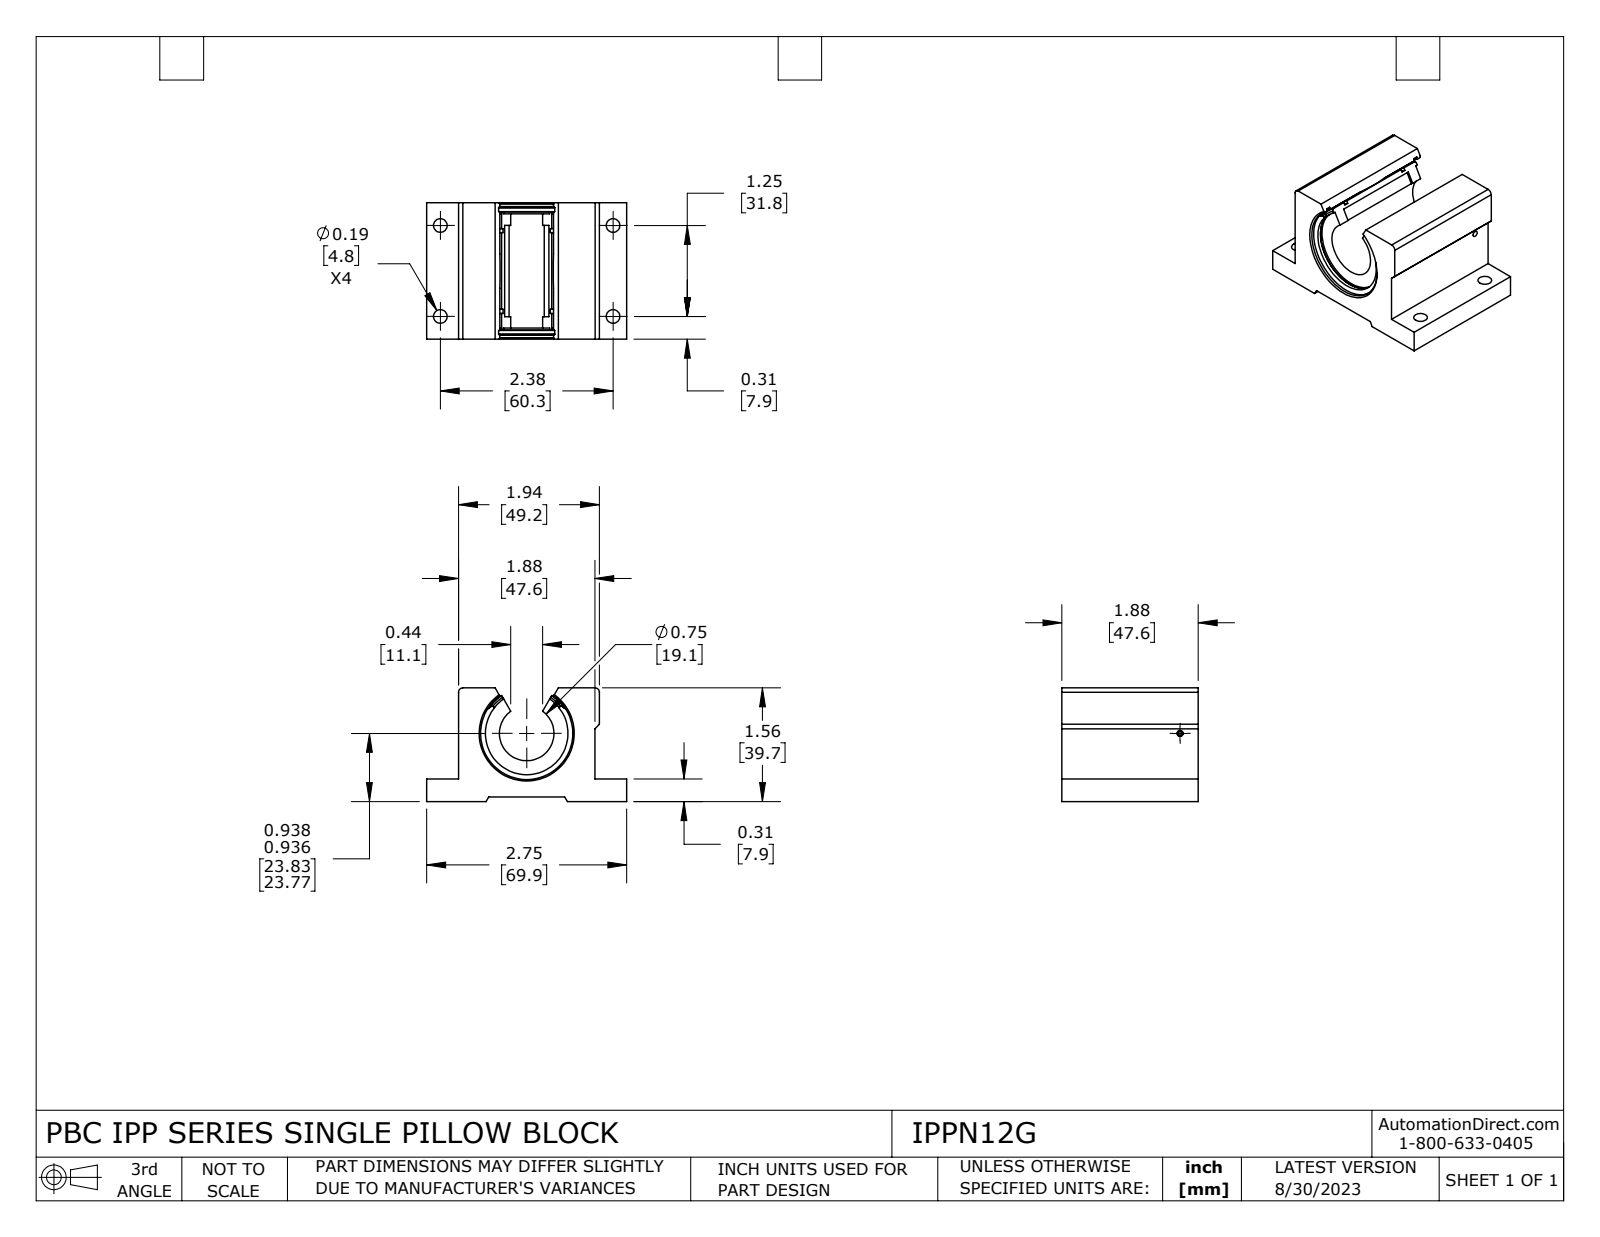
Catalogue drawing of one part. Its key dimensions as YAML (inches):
part_name: "IPPN12G"
step_written_by: "SolidWorks 2021 (CONFIG_CONTROL_DESIGN)"
units: inches
bodies: {solids: 5, faces: 157, planar: 52, cylindrical: 74, other: 31}
overall_size: [2.75, 1.875, 1.563]
volume: 4.483
surface_area: 38.52
round_holes:
  - {diameter: 0.187, count: 4}
  - {diameter: 0.054, count: 1}
  - {diameter: 0.079, count: 1}
  - {diameter: 0.136, count: 1}
  - {diameter: 0.75, count: 1}
  - {diameter: 1.138, count: 1}
  - {diameter: 1.267, count: 1}
  - {diameter: 1.33, count: 1}
round_bosses_or_shafts:
  - {diameter: 1.25, count: 1}
  - {diameter: 1.176, count: 1}
  - {diameter: 0.078, count: 1}
partial_cylinders:
  - {radius: 0.03, count: 2}
  - {radius: 0.06, count: 2}
  - {radius: 0.18, count: 2}
  - {radius: 0.545, count: 1}
  - {radius: 0.567, count: 1}
  - {radius: 0.676, count: 1}
face_to_face_distances: [1.875, 0.065, 1.563, 1.498, 0.247, 0.312, 1.251, 0.437, 2.312, 0.153]
hole_center_spacings: [1.25, 2.375, 2.684]
